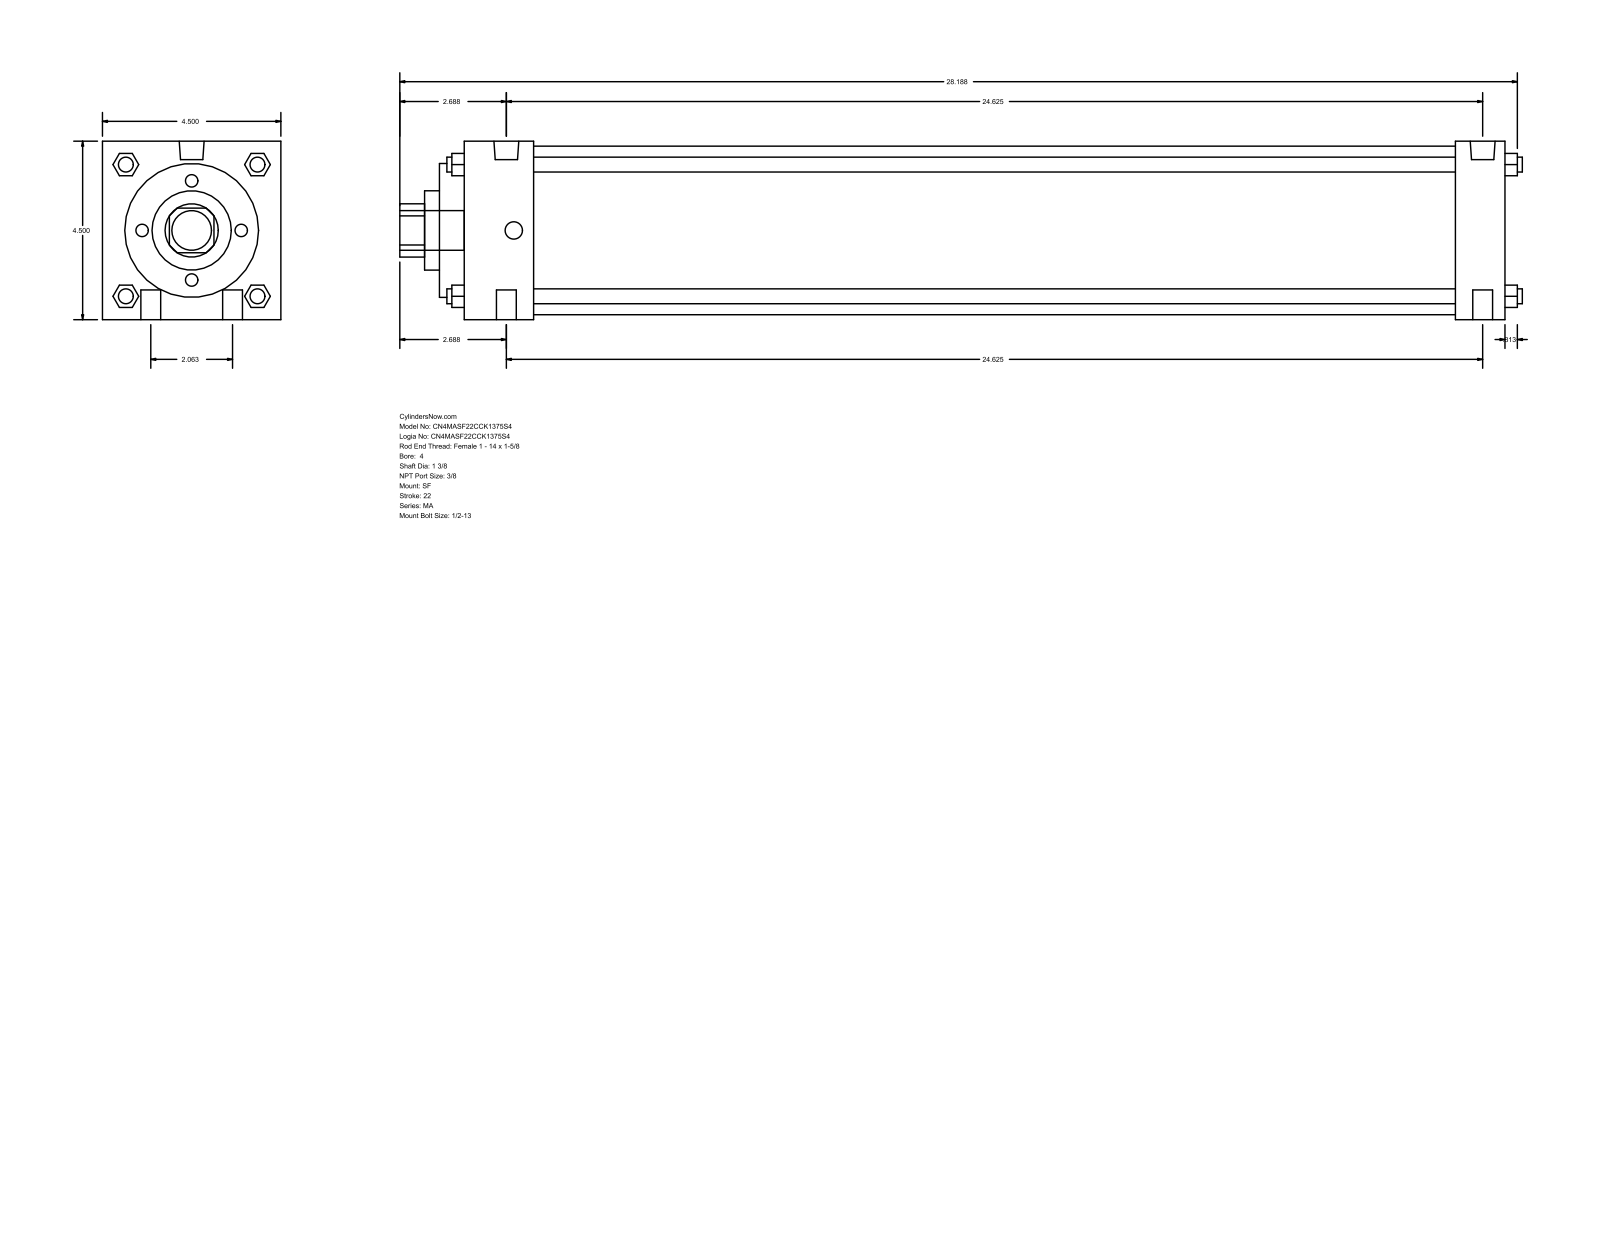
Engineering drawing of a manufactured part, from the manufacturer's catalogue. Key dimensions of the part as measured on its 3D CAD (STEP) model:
Part name (STEP PRODUCT): MA_SF__0400_1.375
STEP written by: GSSL Pune (CONFIG_CONTROL_DESIGN)
Units: millimetres
Bodies: 0 solids, 126 faces (95 planar, 31 cylindrical, 0 other)
Overall size (bounding box): 719.14 × 114.3 × 114.3
Round holes (diameter × count): ⌀34.92 ×1, ⌀50.8 ×1, ⌀85.72 ×1, ⌀107.95 ×1
Round bosses / shafts (diameter × count): ⌀12.7 ×4, ⌀9.53 ×4, ⌀15.93 ×2, ⌀11.11 ×2, ⌀25.4 ×1
Partial cylindrical surfaces — rounded edges, fillets, slot ends (radius × count): R17.06 ×1
Main face-to-face distances: 114.3, 666.75, 682.62, 15.87, 650.87, 635, 31.75, 60.32, 44.45, 590.55
